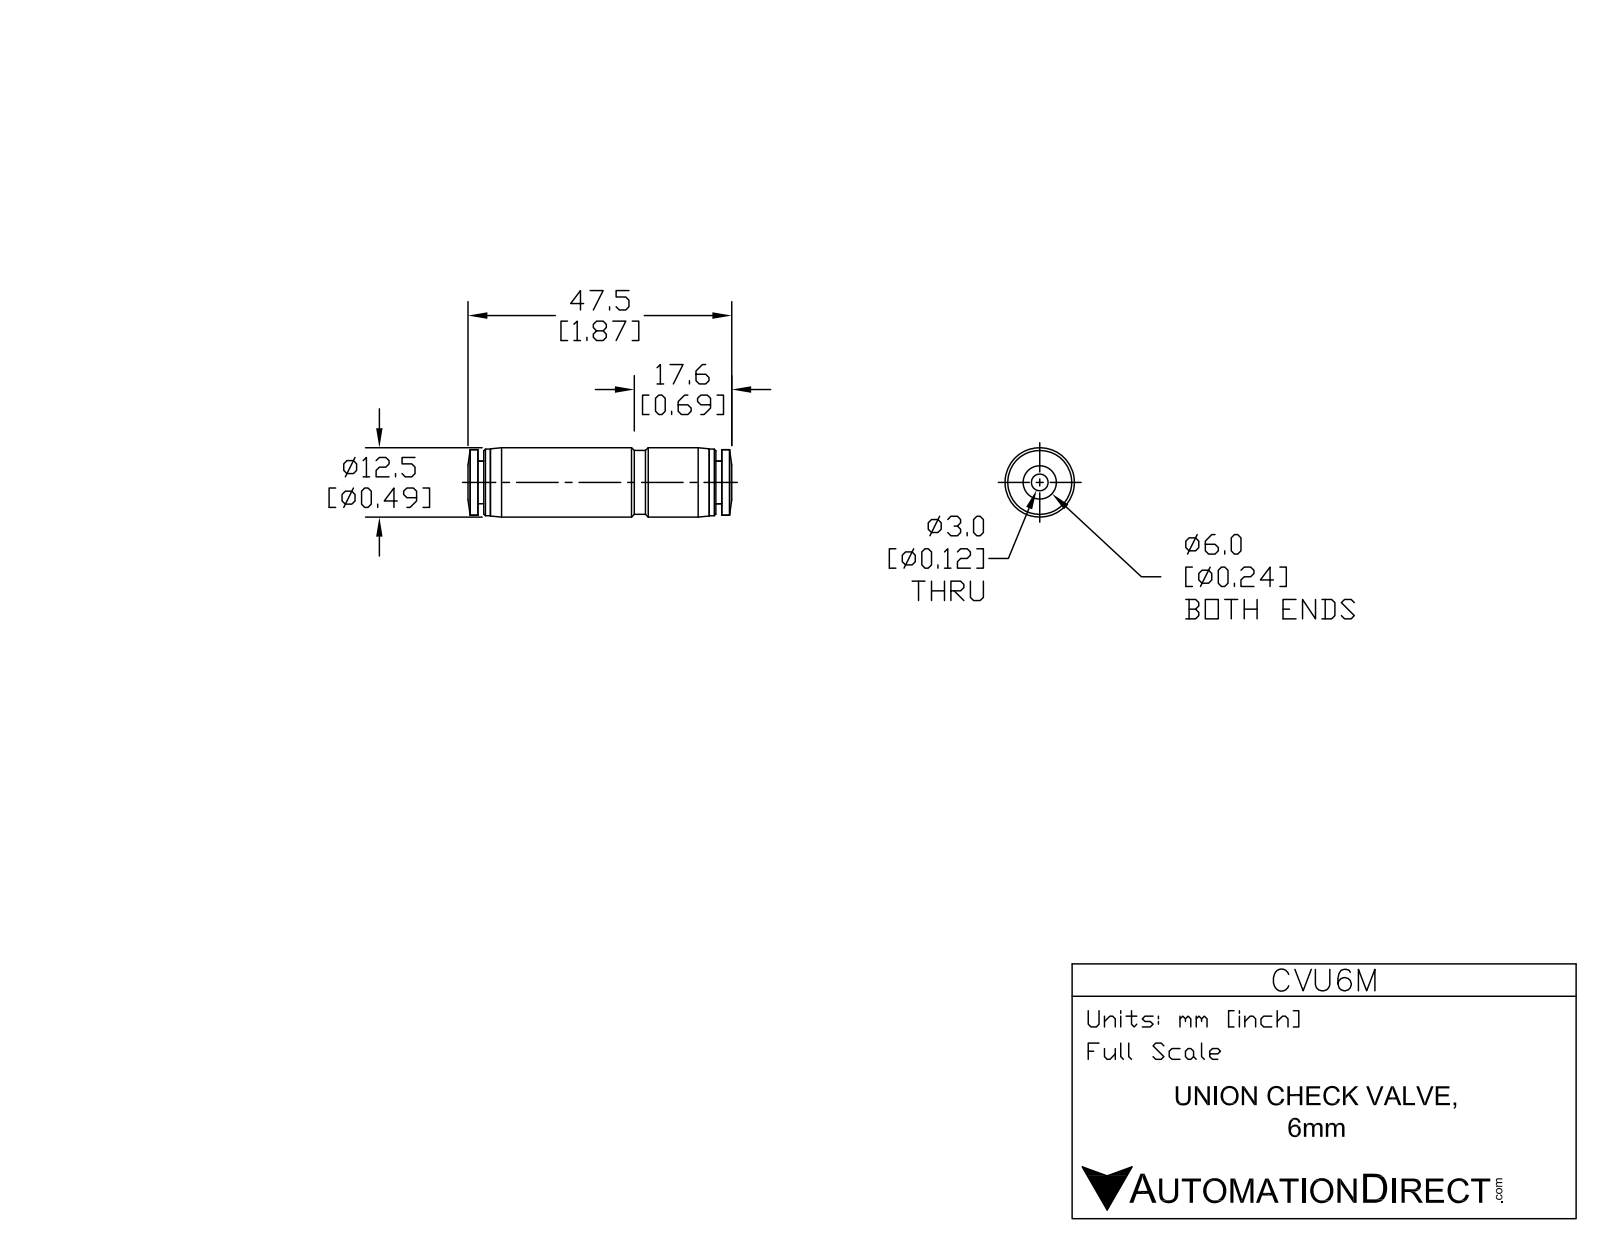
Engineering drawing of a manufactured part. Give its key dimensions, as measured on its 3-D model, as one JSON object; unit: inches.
{"part_name": "CVU6M", "step_written_by": "SolidWorks 2015 (AUTOMOTIVE_DESIGN)", "units": "inches", "bodies": {"solids": 1, "faces": 76, "planar": 24, "cylindrical": 32, "other": 20}, "overall_size": [1.87, 0.492, 0.492], "volume_in3": 0.255, "surface_area_in2": 4.818, "round_holes": [[0.199, 1], [0.248, 1]], "round_bosses_or_shafts": [[0.492, 1], [0.472, 1], [0.465, 1], [0.453, 1], [0.303, 1], [0.11, 1]], "partial_cylinders_radius": [[0.069, 1], [0.242, 1]], "face_to_face_distances": [0.041, 1.687, 1.728, 1.646, 0.575, 1.154, 0.533, 1.112, 0.579, 0.071]}
